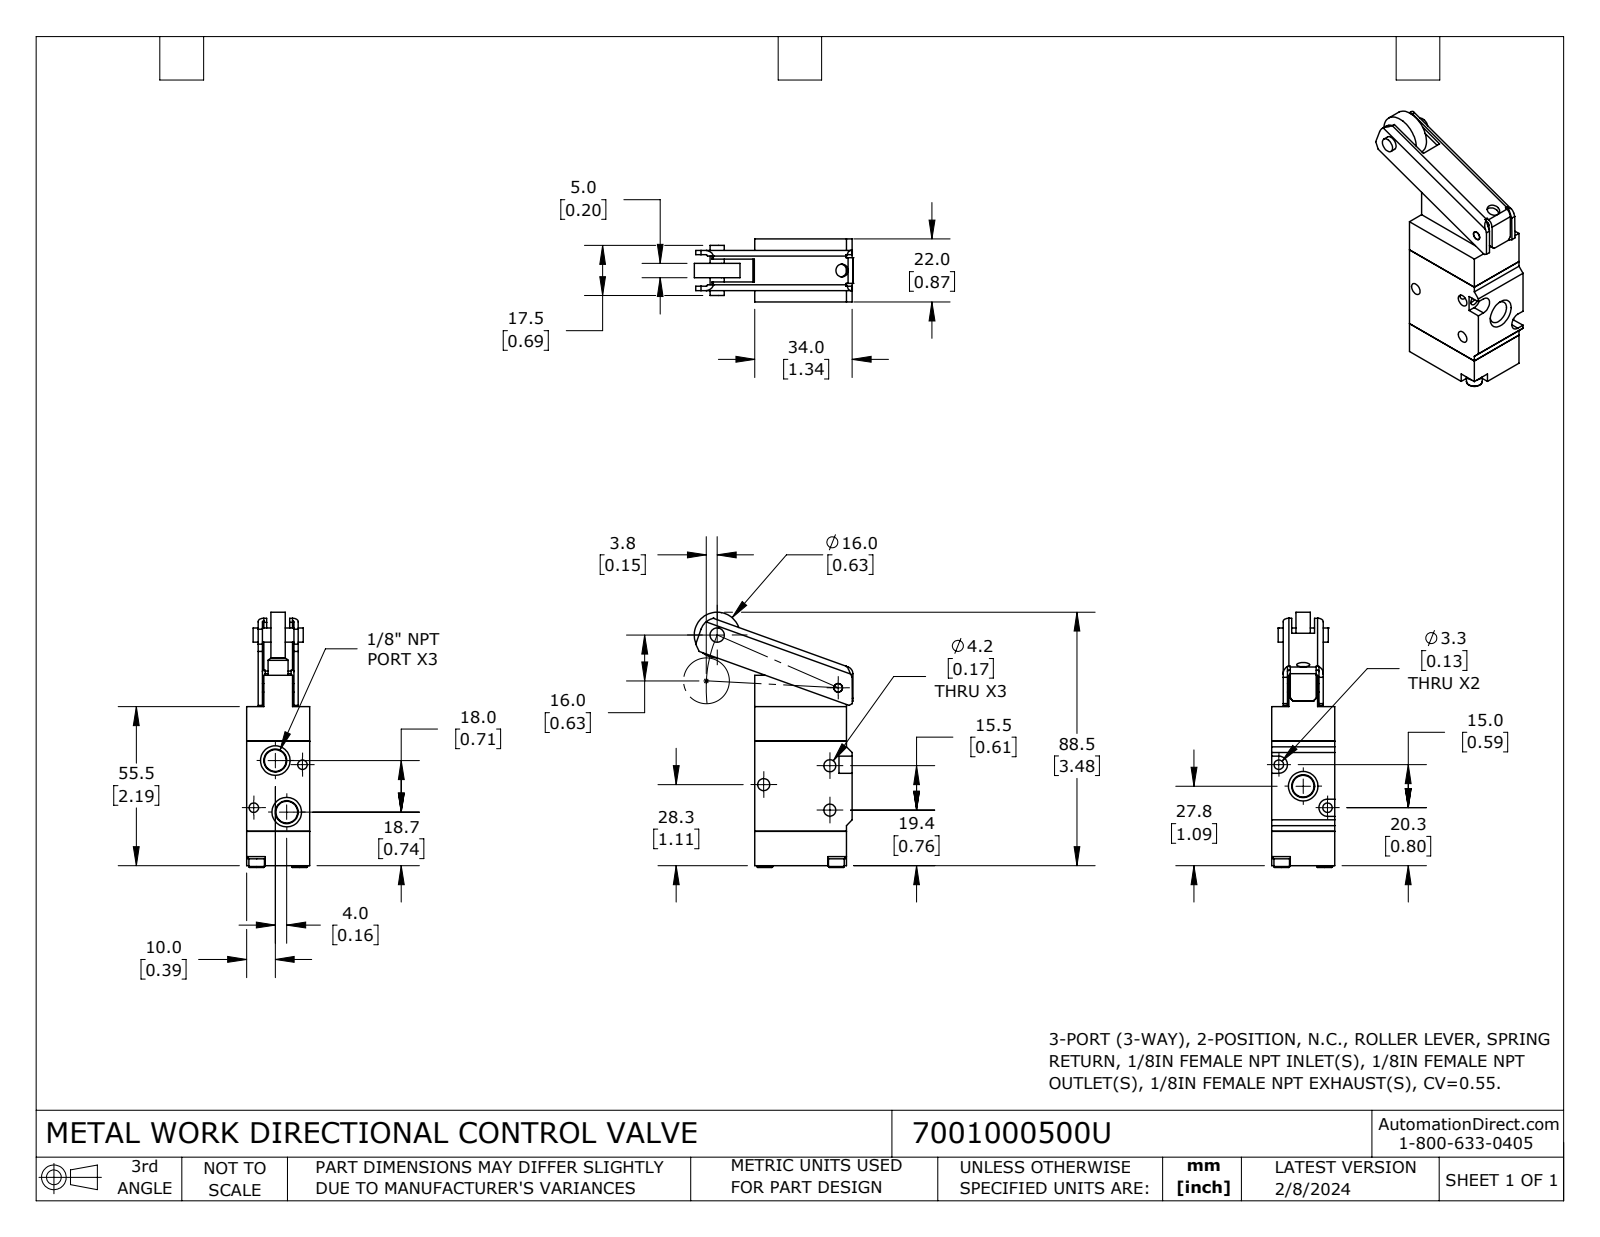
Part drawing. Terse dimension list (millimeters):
name: 7001000500U
written by: SolidWorks 2023 (CONFIG_CONTROL_DESIGN)
unit: mm
bodies: 9 solids, 222 faces (116 planar, 64 cylindrical, 42 other)
size: 89.1 × 55.4 × 22
volume: 45 180 mm³; area: 18 790 mm²
holes: 3× ⌀3, 3× ⌀4.2, 2× ⌀3.3, 1× ⌀4.5, 1× ⌀5
bosses: 2× ⌀6, 2× ⌀5.5, 1× ⌀16, 1× ⌀7
rounds: 2× R0.5, 2× R2, 2× R3, 1× R1, 1× R2.5, 1× R6
face distances: 22, 12, 1.5, 31.5, 4, 18, 5.5, 16.5, 12.5, 2
hole spacings: 15.5, 22.7, 24, 24.8, 27.3, 29.2, 42.6, 42.8
